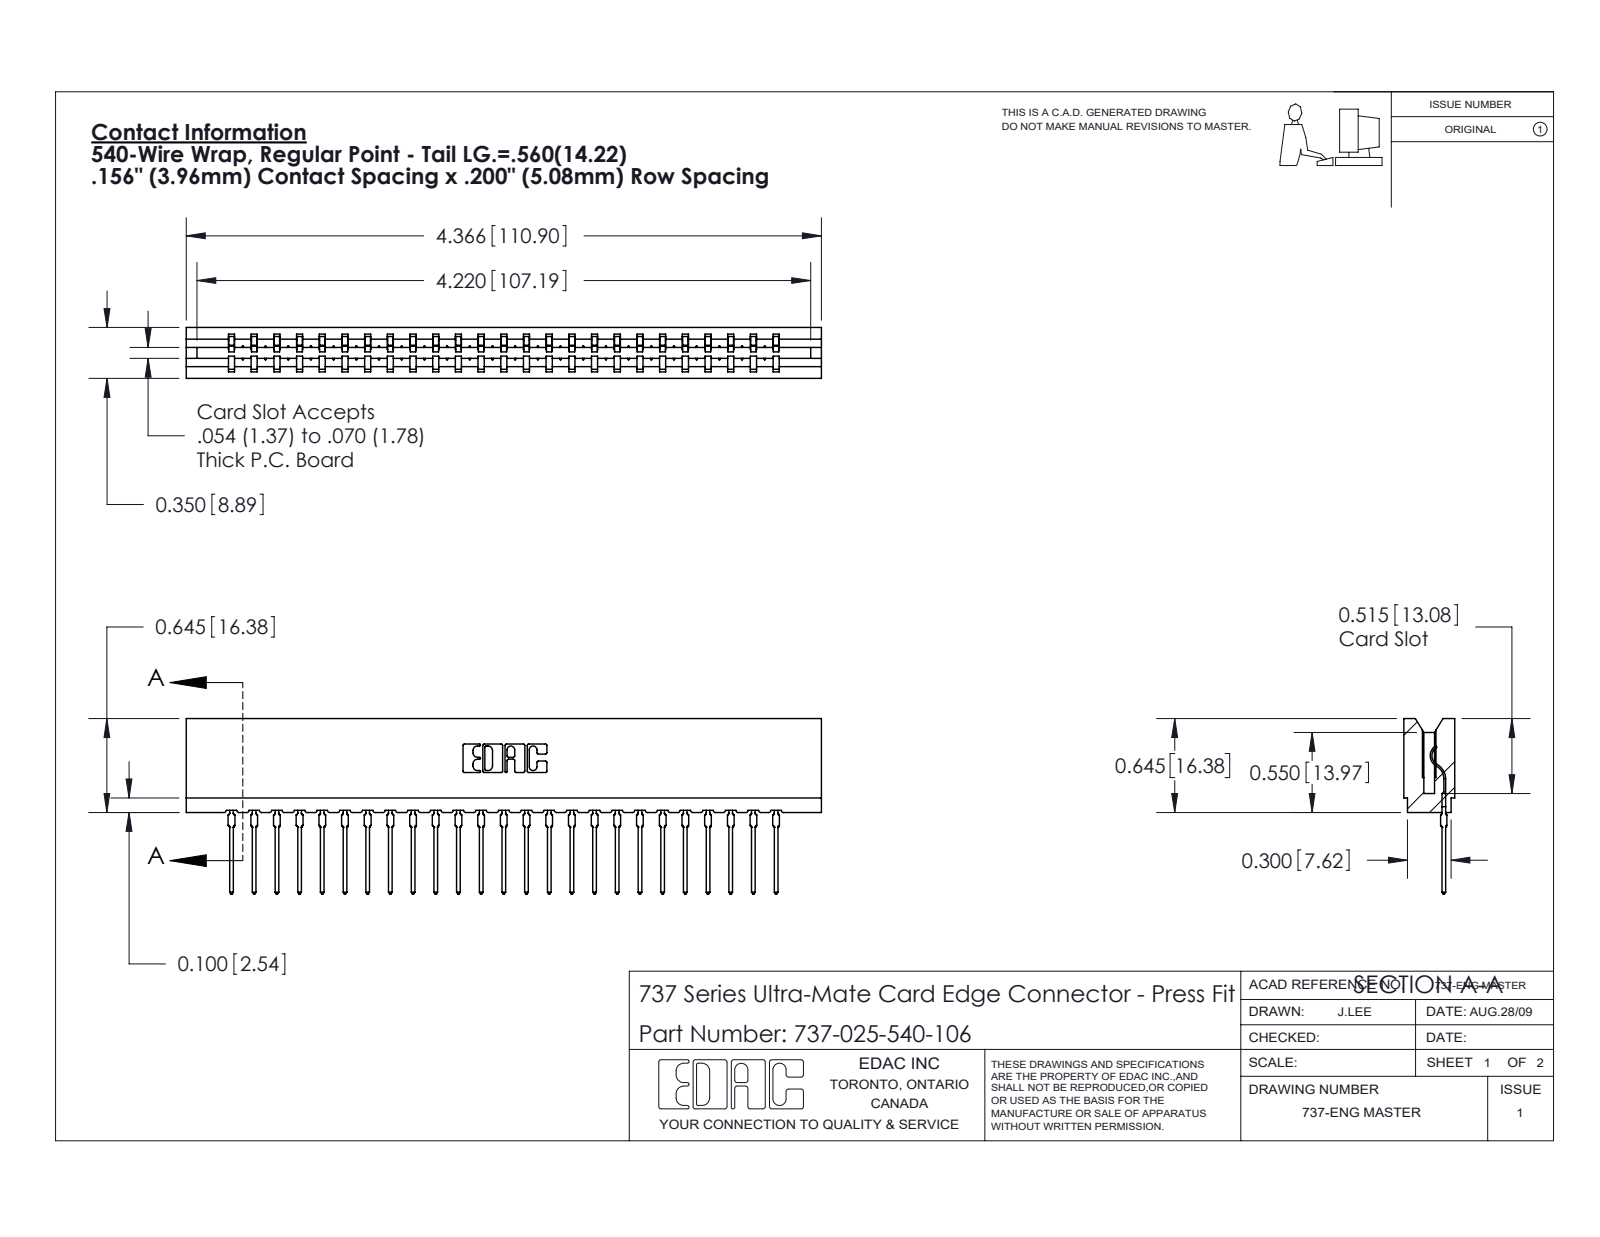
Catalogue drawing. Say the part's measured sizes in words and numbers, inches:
The part is named "737 Part_Insulator Option - 06; 745-292-001_540; 737-025-540-106". Its 3-D file was written by "SolidWorks 2020 (CONFIG_CONTROL_DESIGN)". It is 26 solids with 2920 faces: 1755 planar, 515 cylindrical and 650 other. Overall it measures 4.366 by 1.206 by 0.35 inches. Its volume is 0.664 cubic inches and its surface area 22.64 square inches. Partial cylindrical surfaces (rounded edges, fillets, slot ends): 50 of radius 0.015, 50 of radius 0.021, 22 of radius 0.01, 6 of radius 0.007, 6 of radius 0.031, 4 of radius 0.005, 4 of radius 0.011, 3 of radius 0.026. The main face-to-face distances are 0.138, 0.212, 0.35, 0.156, 0.074, 0.624, 0.045, 0.305, 0.093, 0.167.
